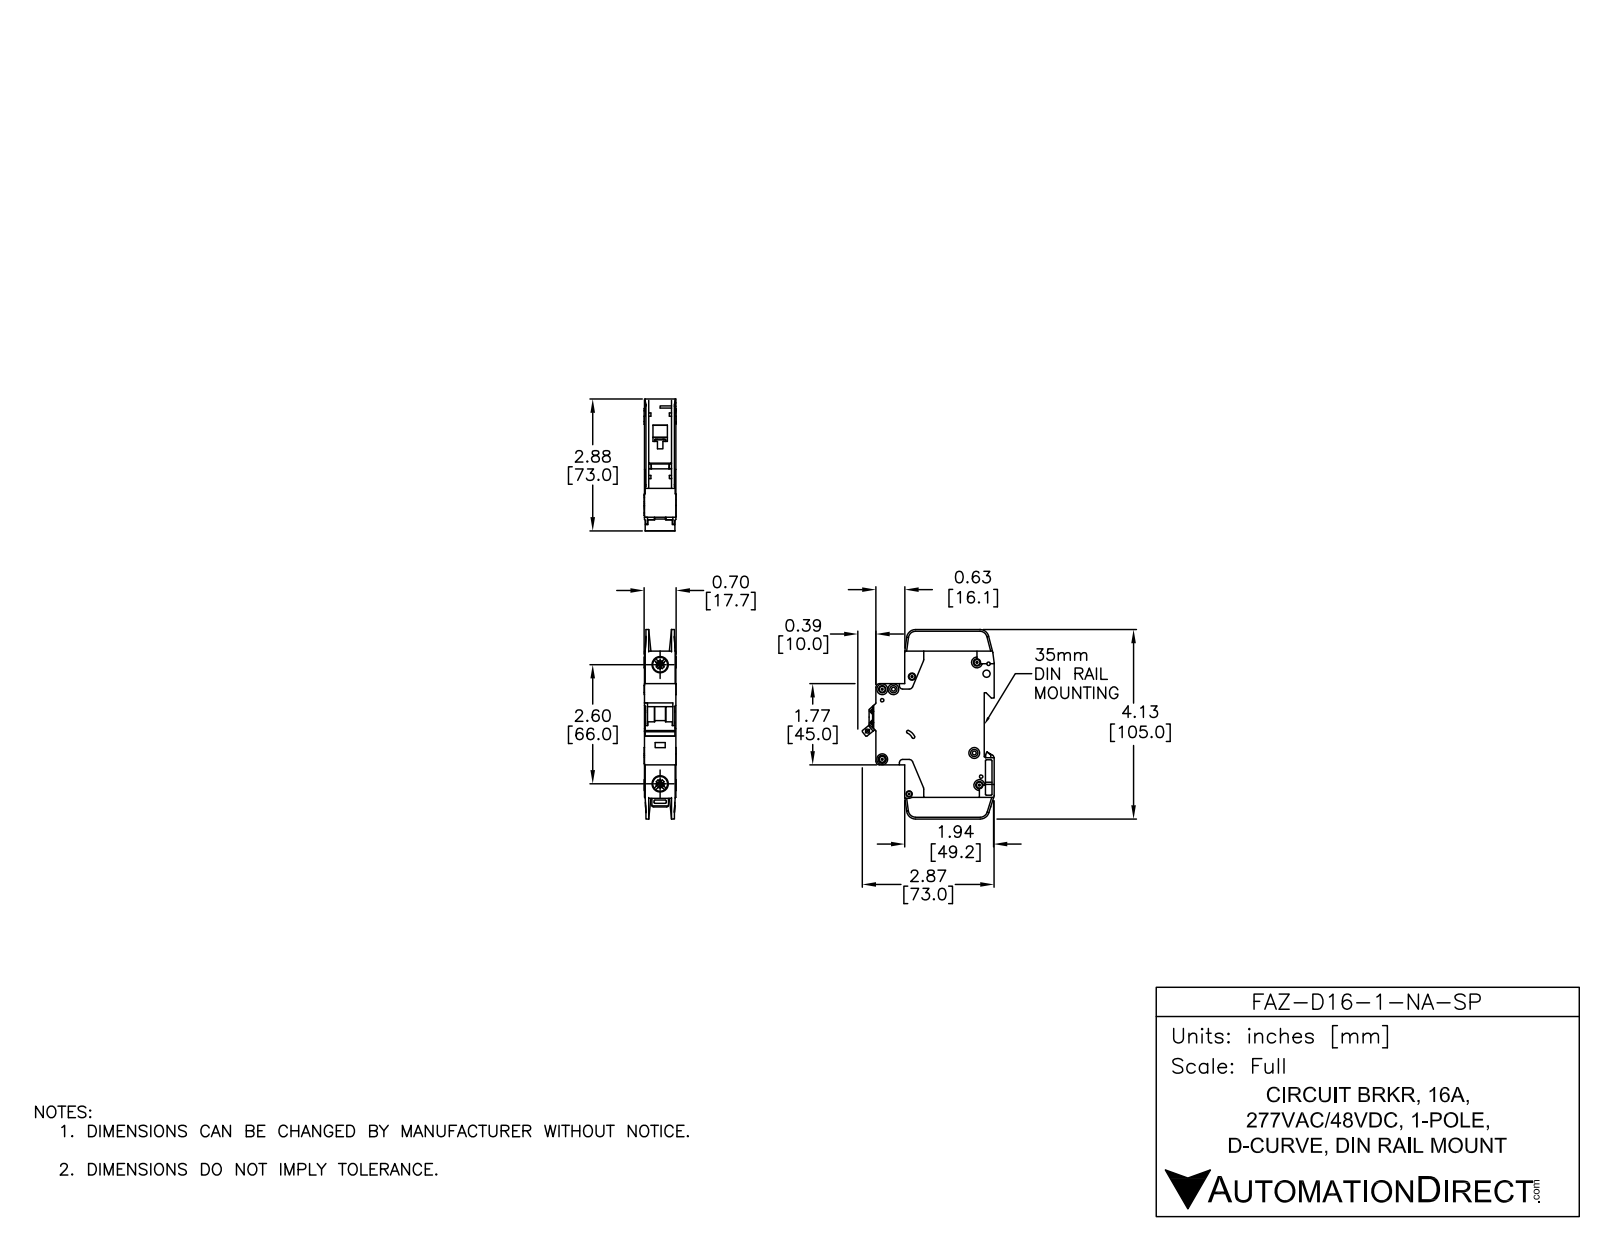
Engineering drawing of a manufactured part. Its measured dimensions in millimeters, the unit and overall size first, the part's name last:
Units: millimetres
Overall size (bounding box): 105 × 73.04 × 17.7
Round holes (diameter × count): ⌀3.6 ×7, ⌀1.09 ×2, ⌀1.5 ×2, ⌀4 ×2, ⌀7.15 ×2, ⌀8.2 ×2, ⌀1.9 ×1, ⌀2.15 ×1, ⌀2.2 ×1, ⌀2.55 ×1, ⌀3.3 ×1, ⌀3.4 ×1
Round bosses / shafts (diameter × count): ⌀6 ×7, ⌀2.5 ×1
Partial cylindrical surfaces — rounded edges, fillets, slot ends (radius × count): R0.25 ×29, R0.5 ×18, R1 ×10, R2 ×10, R5 ×5, R4 ×4, R1.8 ×3, R0.2 ×2
Main face-to-face distances: 17.5, 15.05, 0.7, 2.45, 1.75, 15.75, 13.3, 14, 12.6, 2
Hole centre spacings: 6.2, 5.19, 6.1, 8.19, 8.56, 8.7, 11.11, 12.45
Volume: 77 695 mm³ · Surface area: 24 740 mm²
Bodies: 3 solids, 784 faces (409 planar, 263 cylindrical, 112 other)
Part name (STEP PRODUCT): FAZ-D16-1-NA-SP
STEP written by: SolidWorks 2014 (AUTOMOTIVE_DESIGN)
